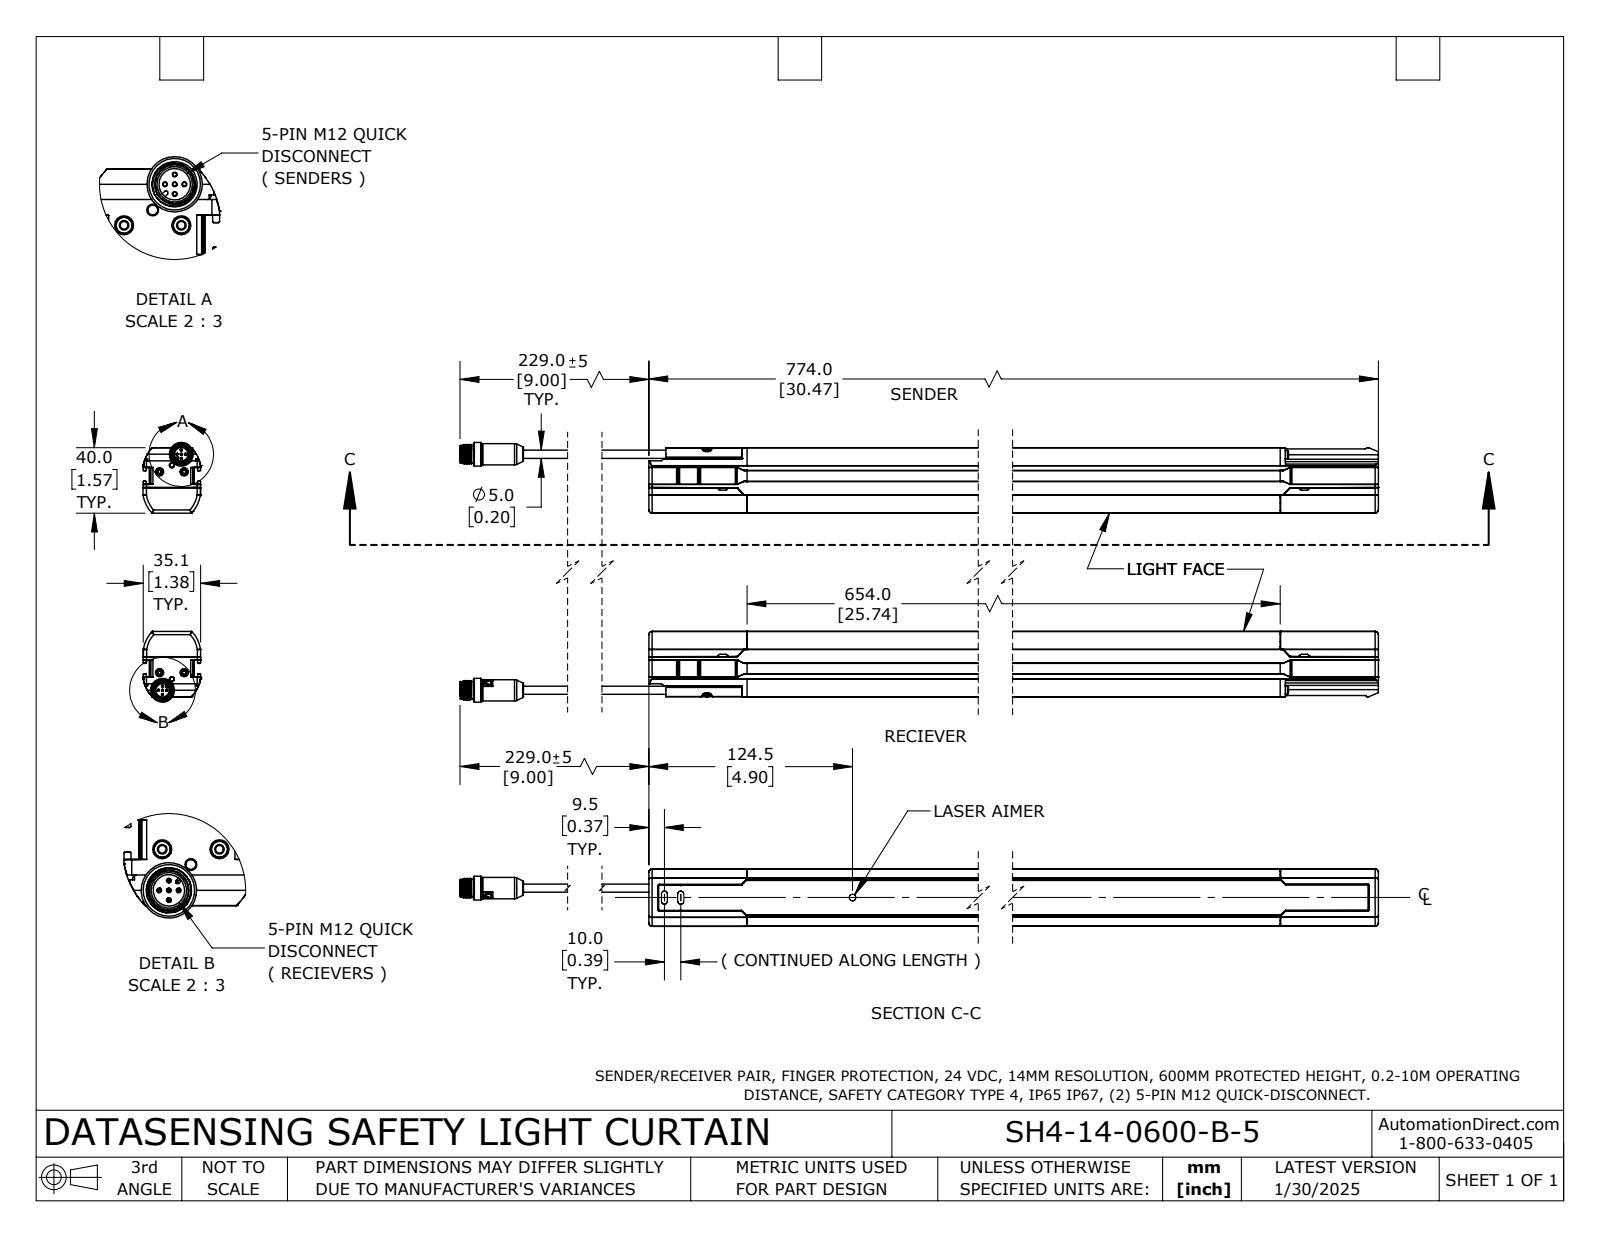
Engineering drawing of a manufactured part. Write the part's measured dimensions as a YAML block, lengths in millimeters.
part_name: "957920003"
step_written_by: "SolidWorks 2024 (AUTOMOTIVE_DESIGN)"
units: millimeters
bodies: {solids: 4, faces: 2582, planar: 1178, cylindrical: 778, other: 626}
overall_size: [837.4, 153.9, 35.2]
volume: 1419000
surface_area: 276800
round_holes:
  - {diameter: 2, count: 6}
  - {diameter: 3, count: 6}
  - {diameter: 5, count: 6}
  - {diameter: 2.6, count: 2}
  - {diameter: 2.6, count: 2}
  - {diameter: 2.6, count: 2}
  - {diameter: 2.6, count: 2}
  - {diameter: 2.8, count: 2}
  - {diameter: 8.3, count: 2}
  - {diameter: 9.7, count: 2}
  - {diameter: 10.3, count: 2}
  - {diameter: 10.8, count: 2}
round_bosses_or_shafts:
  - {diameter: 5, count: 10}
  - {diameter: 1, count: 10}
  - {diameter: 2.2, count: 8}
  - {diameter: 4.4, count: 6}
  - {diameter: 5.5, count: 4}
  - {diameter: 14.5, count: 2}
  - {diameter: 13, count: 2}
  - {diameter: 10.6, count: 2}
partial_cylinders:
  - {radius: 0.3, count: 172}
  - {radius: 0.4, count: 72}
  - {radius: 0.5, count: 50}
  - {radius: 0.2, count: 36}
  - {radius: 0.8, count: 26}
  - {radius: 1.2, count: 16}
  - {radius: 0.8, count: 12}
  - {radius: 2, count: 12}
face_to_face_distances: [38, 114.2, 76.2, 0.7, 35, 152.2, 27.1, 4, 31, 2]
hole_center_spacings: [122.7, 15, 22, 123.6, 139.2, 14.9, 15, 15]
